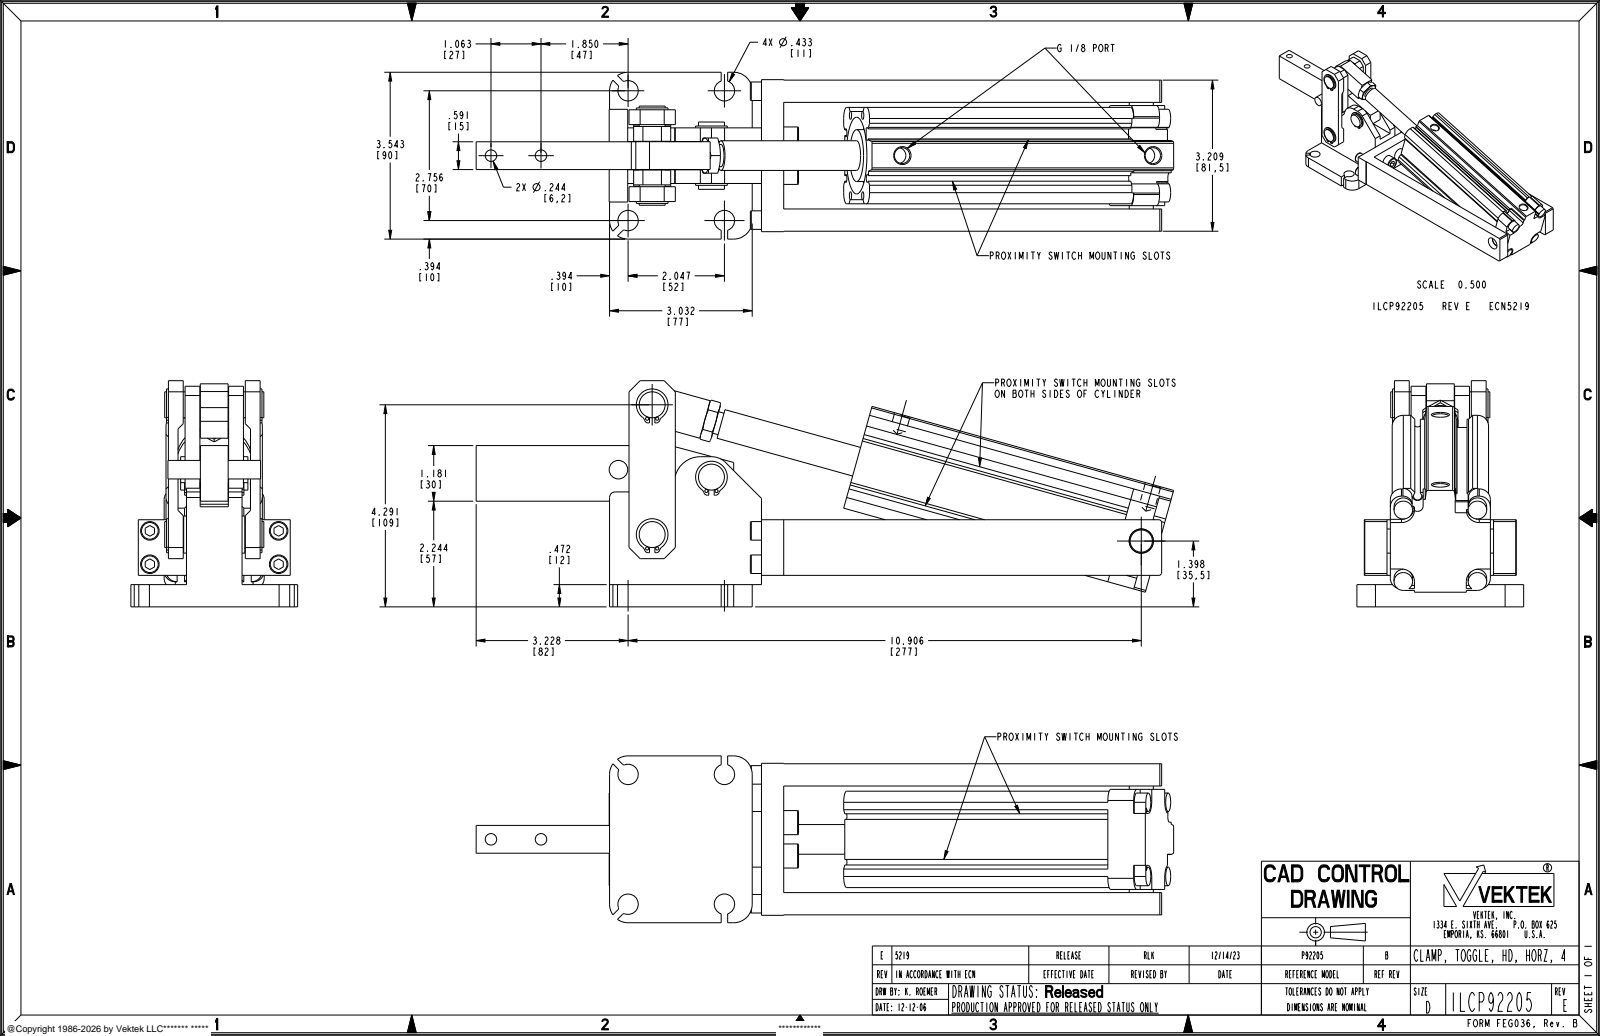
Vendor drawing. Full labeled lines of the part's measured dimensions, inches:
Part name (STEP PRODUCT): ILCP92205
STEP written by: CREO PARAMETRIC BY PTC INC, 2021164 (AUTOMOTIVE_DESIGN)
Units: inches
Bodies: 2 solids, 574 faces (319 planar, 195 cylindrical, 60 other)
Overall size (bounding box): 14.822 × 4.803 × 3.543
Volume: 49.01 in³ · Surface area: 302.6 in²
Round holes (diameter × count): ⌀0.067 ×6, ⌀0.173 ×4, ⌀0.433 ×4, ⌀0.244 ×2, ⌀0.262 ×2, ⌀0.337 ×2, ⌀0.516 ×1, ⌀0.551 ×1, ⌀1.575 ×1, ⌀1.63 ×1
Round bosses / shafts (diameter × count): ⌀0.394 ×9, ⌀0.551 ×4, ⌀0.512 ×3, ⌀1.102 ×1, ⌀0.787 ×1, ⌀0.63 ×1, ⌀0.472 ×1
Partial cylindrical surfaces — rounded edges, fillets, slot ends (radius × count): R0.118 ×8, R0.236 ×8, R0.039 ×6, R0.079 ×6, R0.394 ×5, R0.276 ×4, R0.087 ×3, R0.337 ×3
Main face-to-face distances: 0.472, 2.736, 1.181, 0.669, 0.197, 0.541, 0.886, 1.014, 2.195, 1.722
Hole centre spacings: 2.756, 0.213, 0.969, 1.709, 1.754, 1.965, 1.986, 2.047
